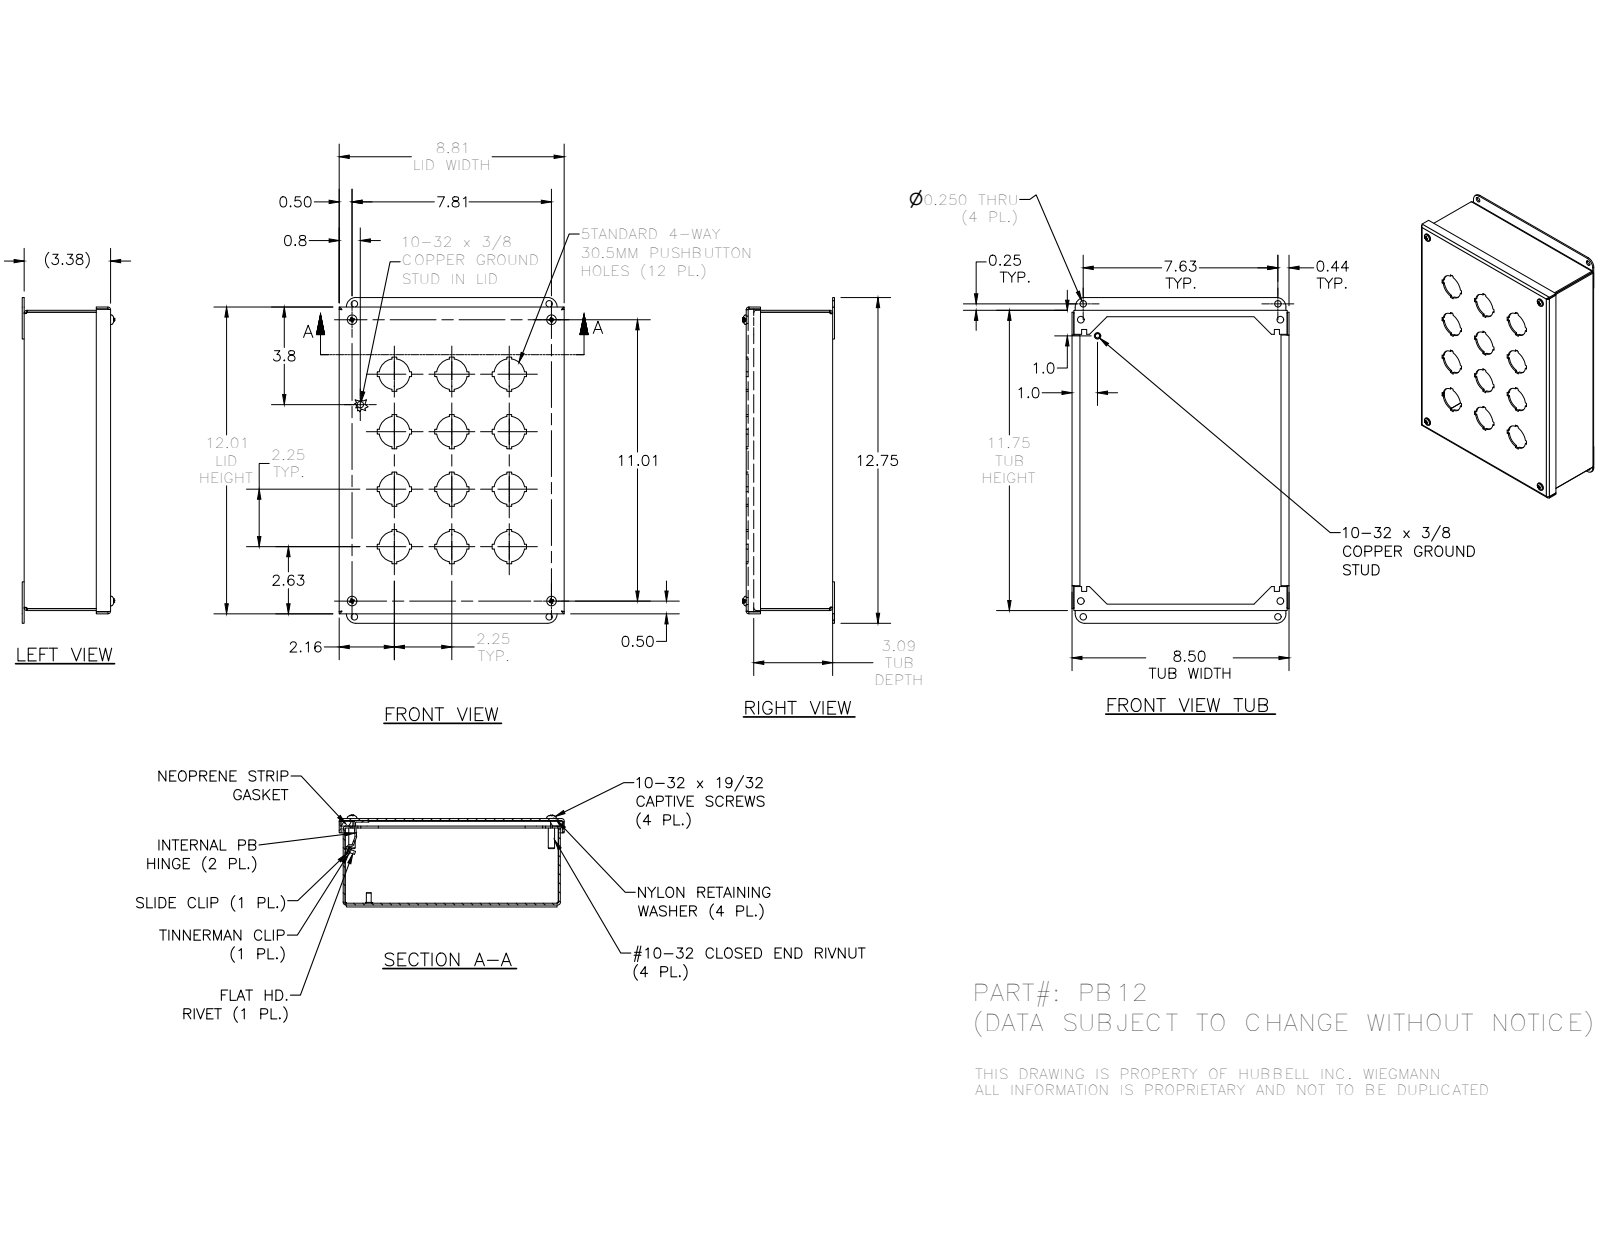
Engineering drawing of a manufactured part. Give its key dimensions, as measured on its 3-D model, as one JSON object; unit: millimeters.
{"part_name": "PB12LID; 3285; 39077; 316245 (+8 more)", "step_written_by": "Autodesk Inventor 2016 (AUTOMOTIVE_DESIGN)", "units": "millimeters", "bodies": {"solids": 25, "faces": 813, "planar": 507, "cylindrical": 192, "other": 114}, "overall_size": [323.85, 223.77, 91.13], "volume_mm3": 522294, "surface_area_mm2": 533846, "round_holes": [[30.48, 12], [3.96, 4], [4.98, 4], [6.35, 4], [6.53, 4], [7.06, 4], [7.14, 4], [7.95, 4], [3.56, 2]], "round_bosses_or_shafts": [[4.83, 6], [11.51, 4], [10.31, 4], [9.47, 4], [6.3, 4], [6.35, 3], [3.17, 1]], "partial_cylinders_radius": [[0.79, 12], [2.67, 12], [1.78, 8], [4.78, 6], [2.27, 4], [2.29, 4], [9.53, 4], [0.8, 3]], "face_to_face_distances": [1.88, 84.07, 85.95, 82.19, 214.02, 296.57, 7.46, 76.61, 78.49, 212.14], "hole_center_spacings": [57.15, 127.79, 80.82, 114.3, 15.92, 161.64, 180.72, 196.69]}
